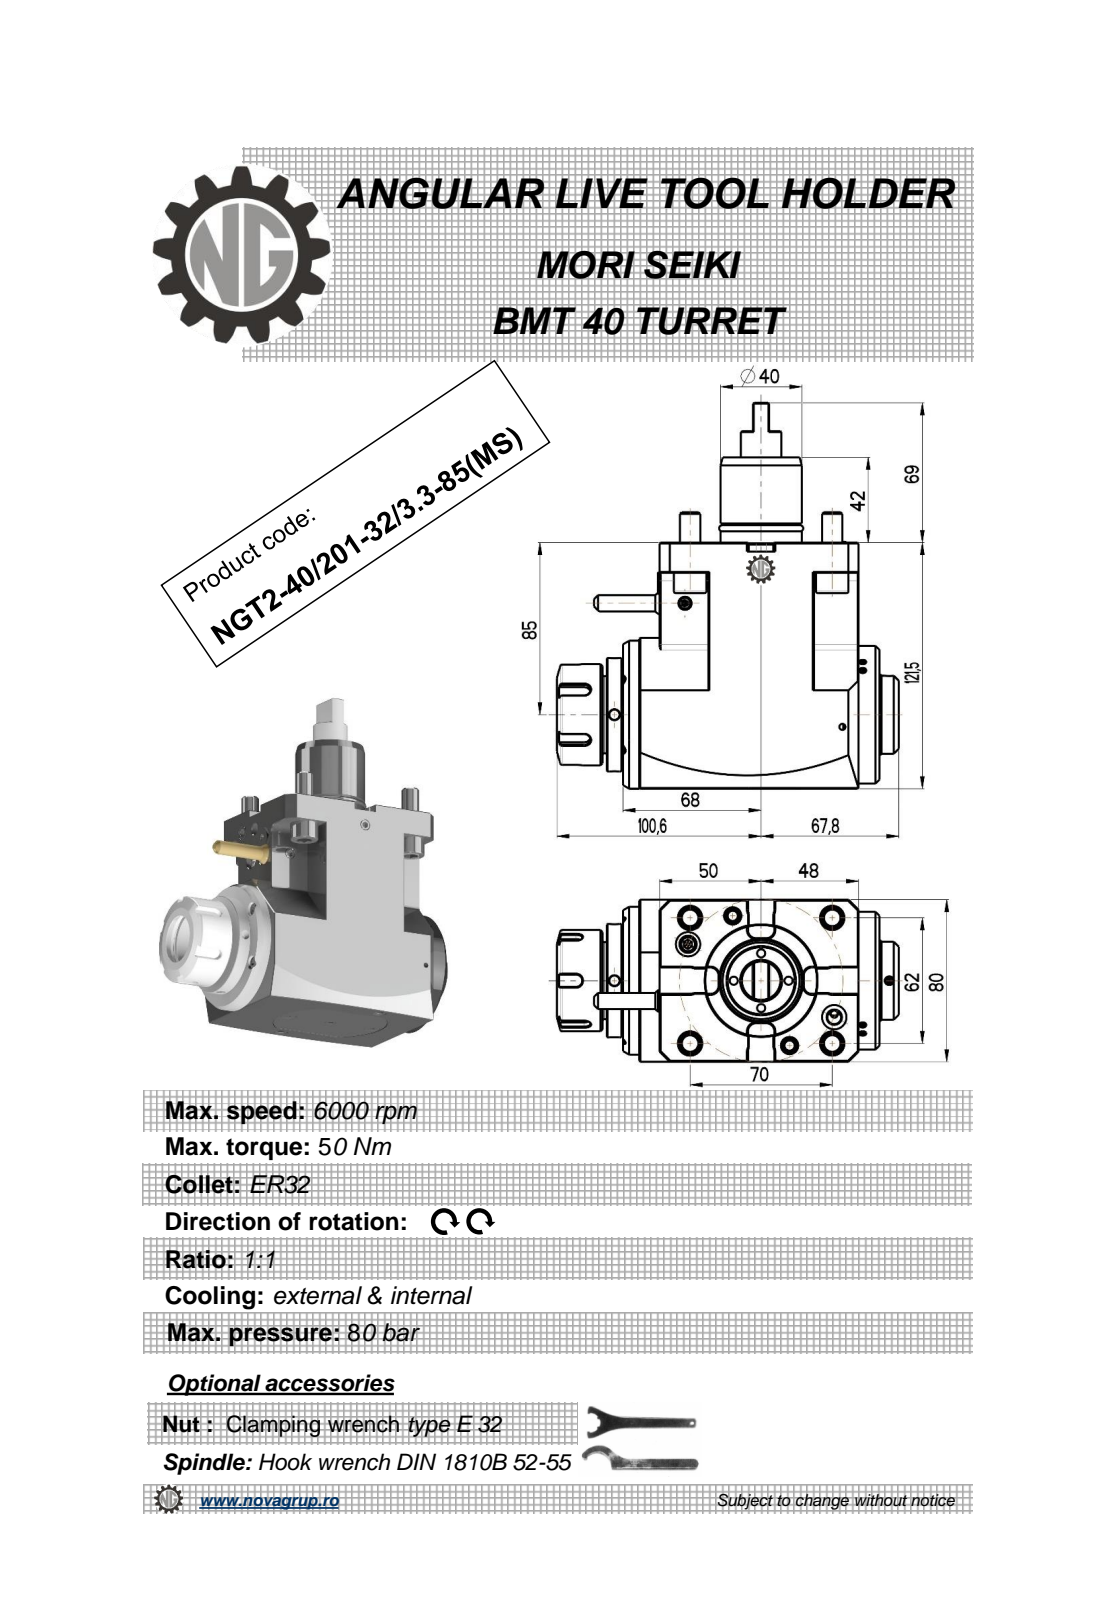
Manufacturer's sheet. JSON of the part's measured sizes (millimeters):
{"part_name": "NGT2_40_201_32_3_3_85_MS", "step_written_by": "PRO/ENGINEER BY PARAMETRIC TECHNOLOGY CORPORATION, 2010280 (CONFIG_CONTROL_DESIGN)", "units": "millimeters", "bodies": {"solids": 2, "faces": 466, "planar": 178, "cylindrical": 104, "other": 184}, "overall_size": [190.5, 168.4, 80], "volume_mm3": 1104000, "surface_area_mm2": 95040, "round_holes": [[5, 3], [6.8, 2], [3, 1], [27, 1]], "round_bosses_or_shafts": [[16, 4], [10, 4], [73, 1], [68, 1], [56, 1], [50, 1], [43.4, 1], [41, 1]], "partial_cylinders_radius": [[4, 20], [3, 5], [0.8, 2], [480, 2], [27.5, 1]], "face_to_face_distances": [80, 121.5, 21, 42, 59, 18, 8, 116, 22, 15], "hole_center_spacings": [40.47, 55.9, 80.5, 109.74]}
